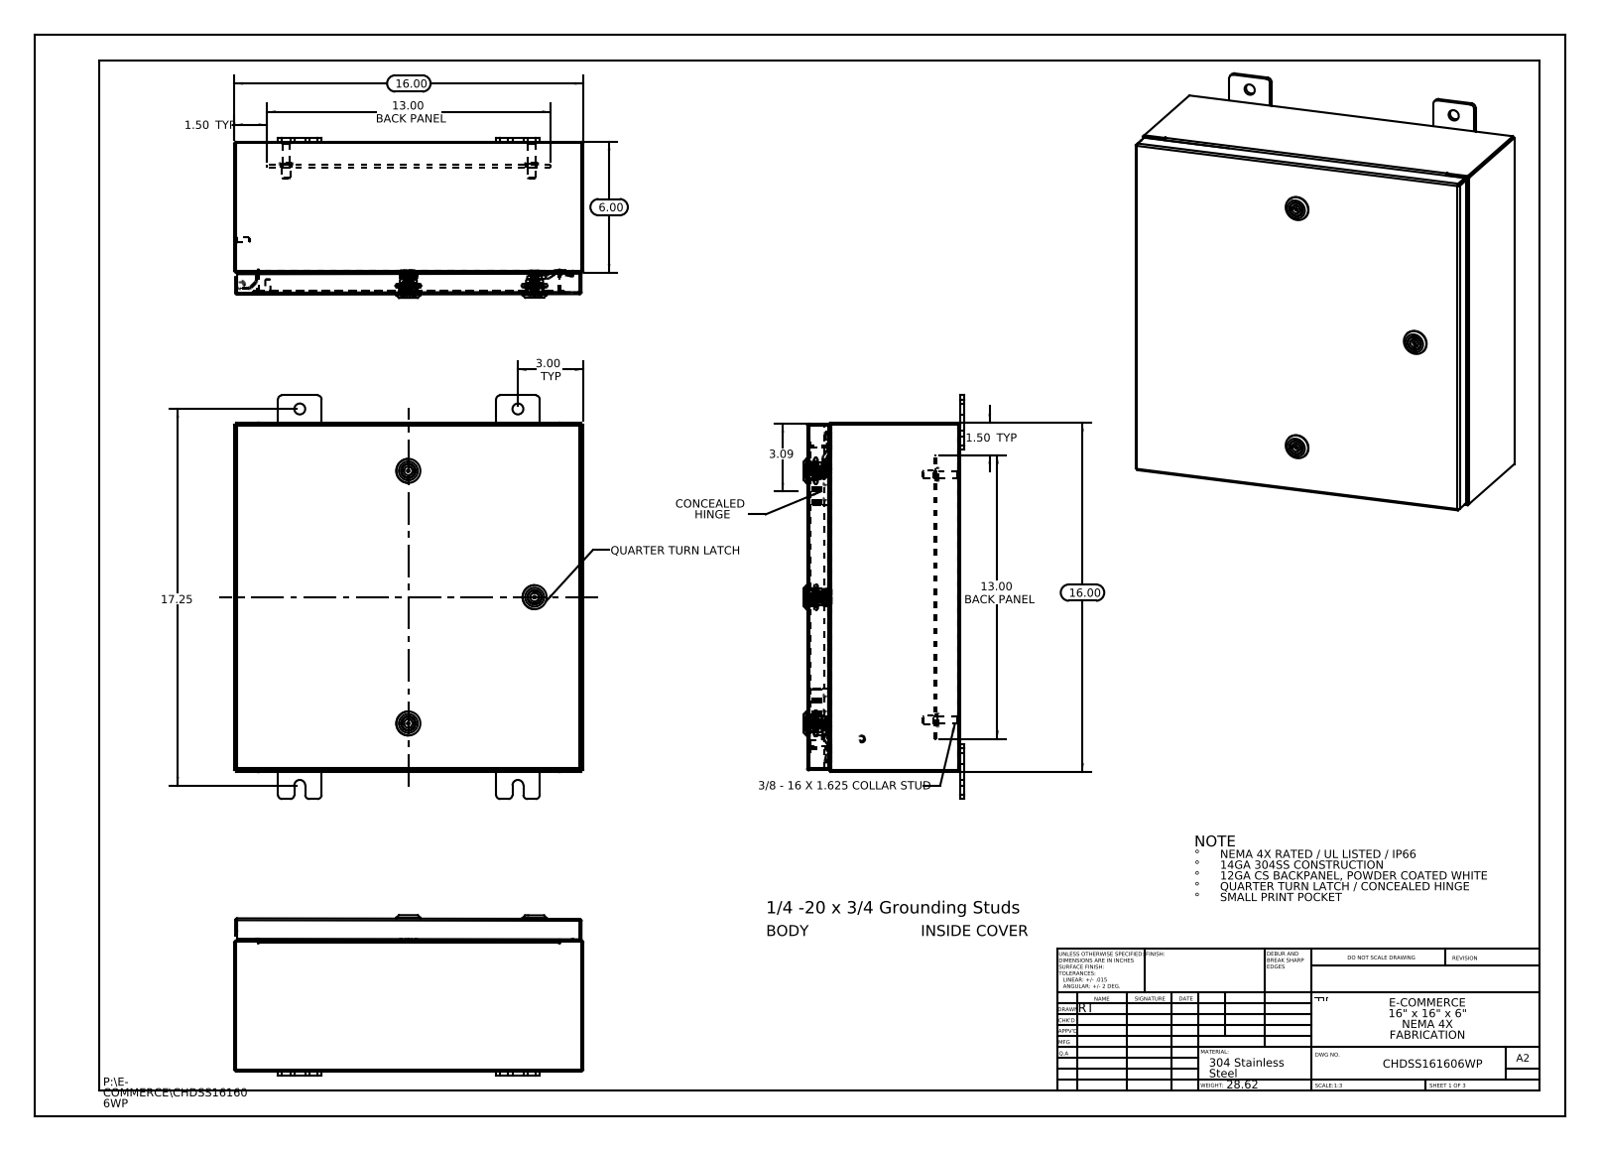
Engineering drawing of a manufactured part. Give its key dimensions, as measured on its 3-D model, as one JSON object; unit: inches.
{"part_name": "CHDSS161606WP Body; CHD161606WP; Housing-211301-IB-Industrilas_Housing-211301-IB-Industrilas; Insert-221320-IB-Industrilas_Insert-221320-IB-Industrilas (+8 more)", "step_written_by": "SolidWorks 2013 (CONFIG_CONTROL_DESIGN)", "units": "inches", "bodies": {"solids": 35, "faces": 2922, "planar": 910, "cylindrical": 914, "other": 1098}, "overall_size": [18.5, 16, 7.345], "volume_in3": 102.4, "surface_area_in2": 2574, "round_holes": [[0.5, 8], [0.394, 6], [0.136, 4], [0.197, 3], [0.4, 3], [0.63, 3], [0.787, 3]], "round_bosses_or_shafts": [[0.236, 5], [0.625, 4], [0.375, 4], [0.33, 4], [1.102, 3], [0.78, 3], [0.626, 3], [0.61, 3]], "partial_cylinders_radius": [[0.006, 99], [0.118, 99], [0.028, 36], [0.19, 24], [0.013, 18], [0.088, 18], [0.02, 12], [0.197, 12]], "face_to_face_distances": [0.075, 15.925, 15.85, 16, 1, 1.075, 1.179, 1.104, 0.104, 5.925], "hole_center_spacings": [11.576, 8.185, 8.184, 1.858, 3.065, 8.185, 8.186, 8.186]}
